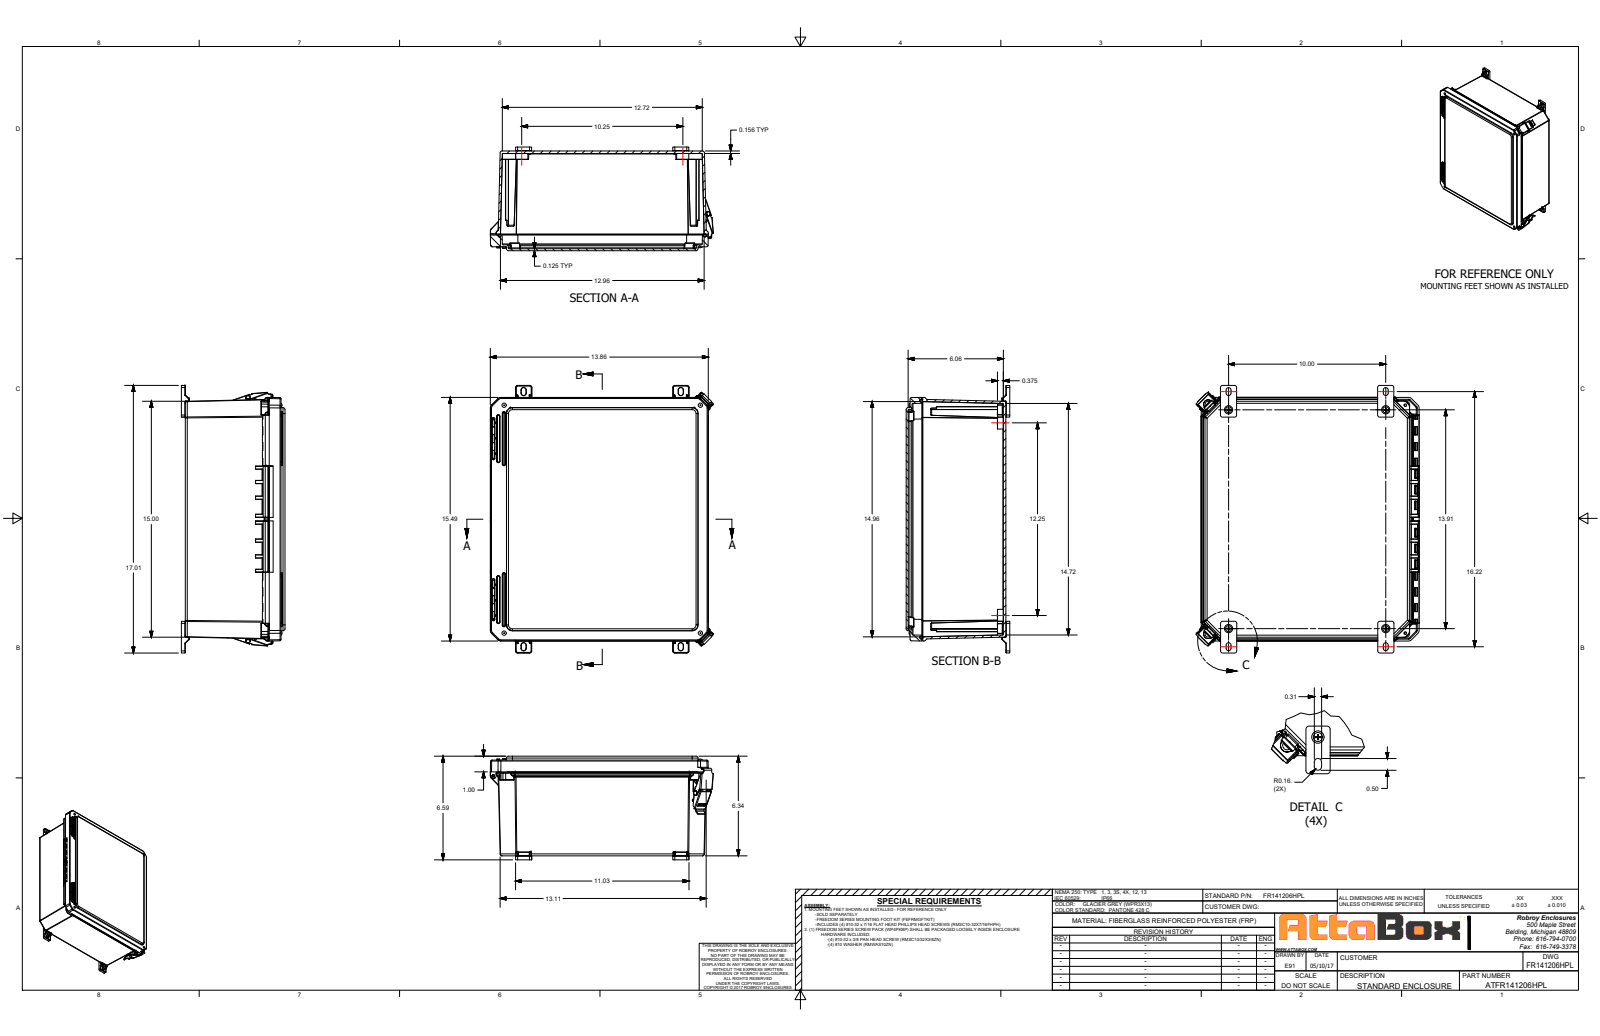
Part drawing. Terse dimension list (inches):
name: FR141206HPL
written by: SolidWorks 2021 (AUTOMOTIVE_DESIGN)
unit: in
bodies: 29 solids, 2484 faces (795 planar, 1065 cylindrical, 624 other)
size: 16.13 × 14.181 × 6.768
volume: 121.3 in³; area: 1 631 in²
holes: 8× ⌀0.135, 8× ⌀0.152, 8× ⌀0.159, 4× ⌀0.135, 4× ⌀0.15, 4× ⌀0.156, 4× ⌀0.252, 4× ⌀0.253, 3× ⌀0.137, 2× ⌀0.219, 2× ⌀0.227, 2× ⌀0.313
bosses: 8× ⌀0.27, 4× ⌀0.87, 4× ⌀0.3, 4× ⌀0.262, 4× ⌀0.209, 3× ⌀0.135, 2× ⌀0.435, 1× ⌀0.135
rounds: 193× R0.01, 110× R0.005, 69× R0.03, 54× R0.02, 36× R0.06, 26× R0.09, 24× R0.03, 24× R0.096
face distances: 0.156, 0.125, 6.184, 6.339, 6.059, 6.215, 0.14, 0.138, 0.139, 0.25
hole spacings: 14.489, 14.254, 13.416, 1.581, 10.16, 13.416, 14.488, 17.55
